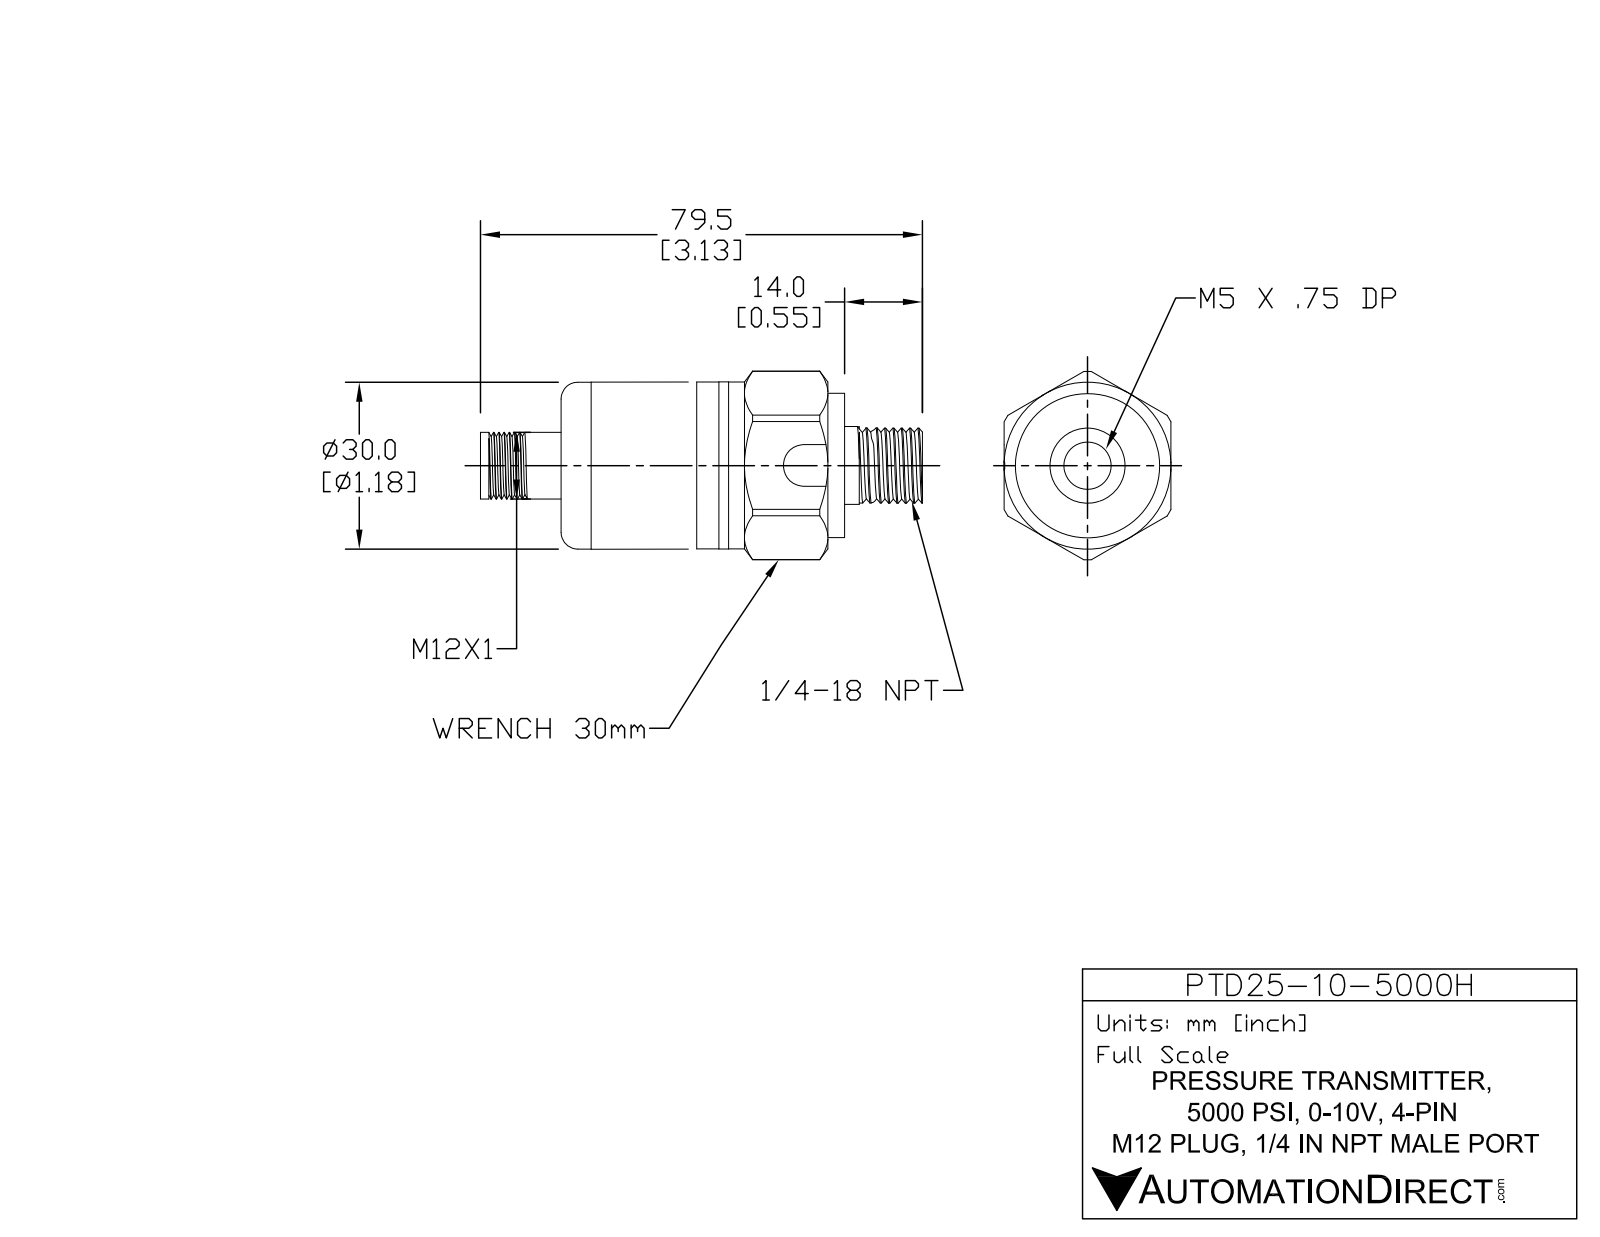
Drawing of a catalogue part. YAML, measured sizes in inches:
part_name: "PTD25-10-5000H"
step_written_by: "SolidWorks 2017 (AUTOMOTIVE_DESIGN)"
units: inches
bodies: {solids: 1, faces: 124, planar: 36, cylindrical: 59, other: 29}
overall_size: [3.13, 1.33, 1.248]
volume: 2.393
surface_area: 12.54
round_holes:
  - {diameter: 0.157, count: 1}
  - {diameter: 0.335, count: 1}
round_bosses_or_shafts:
  - {diameter: 1.183, count: 1}
  - {diameter: 1.181, count: 1}
  - {diameter: 1.022, count: 1}
  - {diameter: 0.551, count: 1}
  - {diameter: 0.531, count: 1}
  - {diameter: 0.472, count: 1}
partial_cylinders:
  - {radius: 0.148, count: 1}
  - {radius: 0.667, count: 1}
face_to_face_distances: [2.008, 1.18, 1.181, 1.89, 0.118, 2.559, 0.669, 0.551, 1.181, 0.222]
